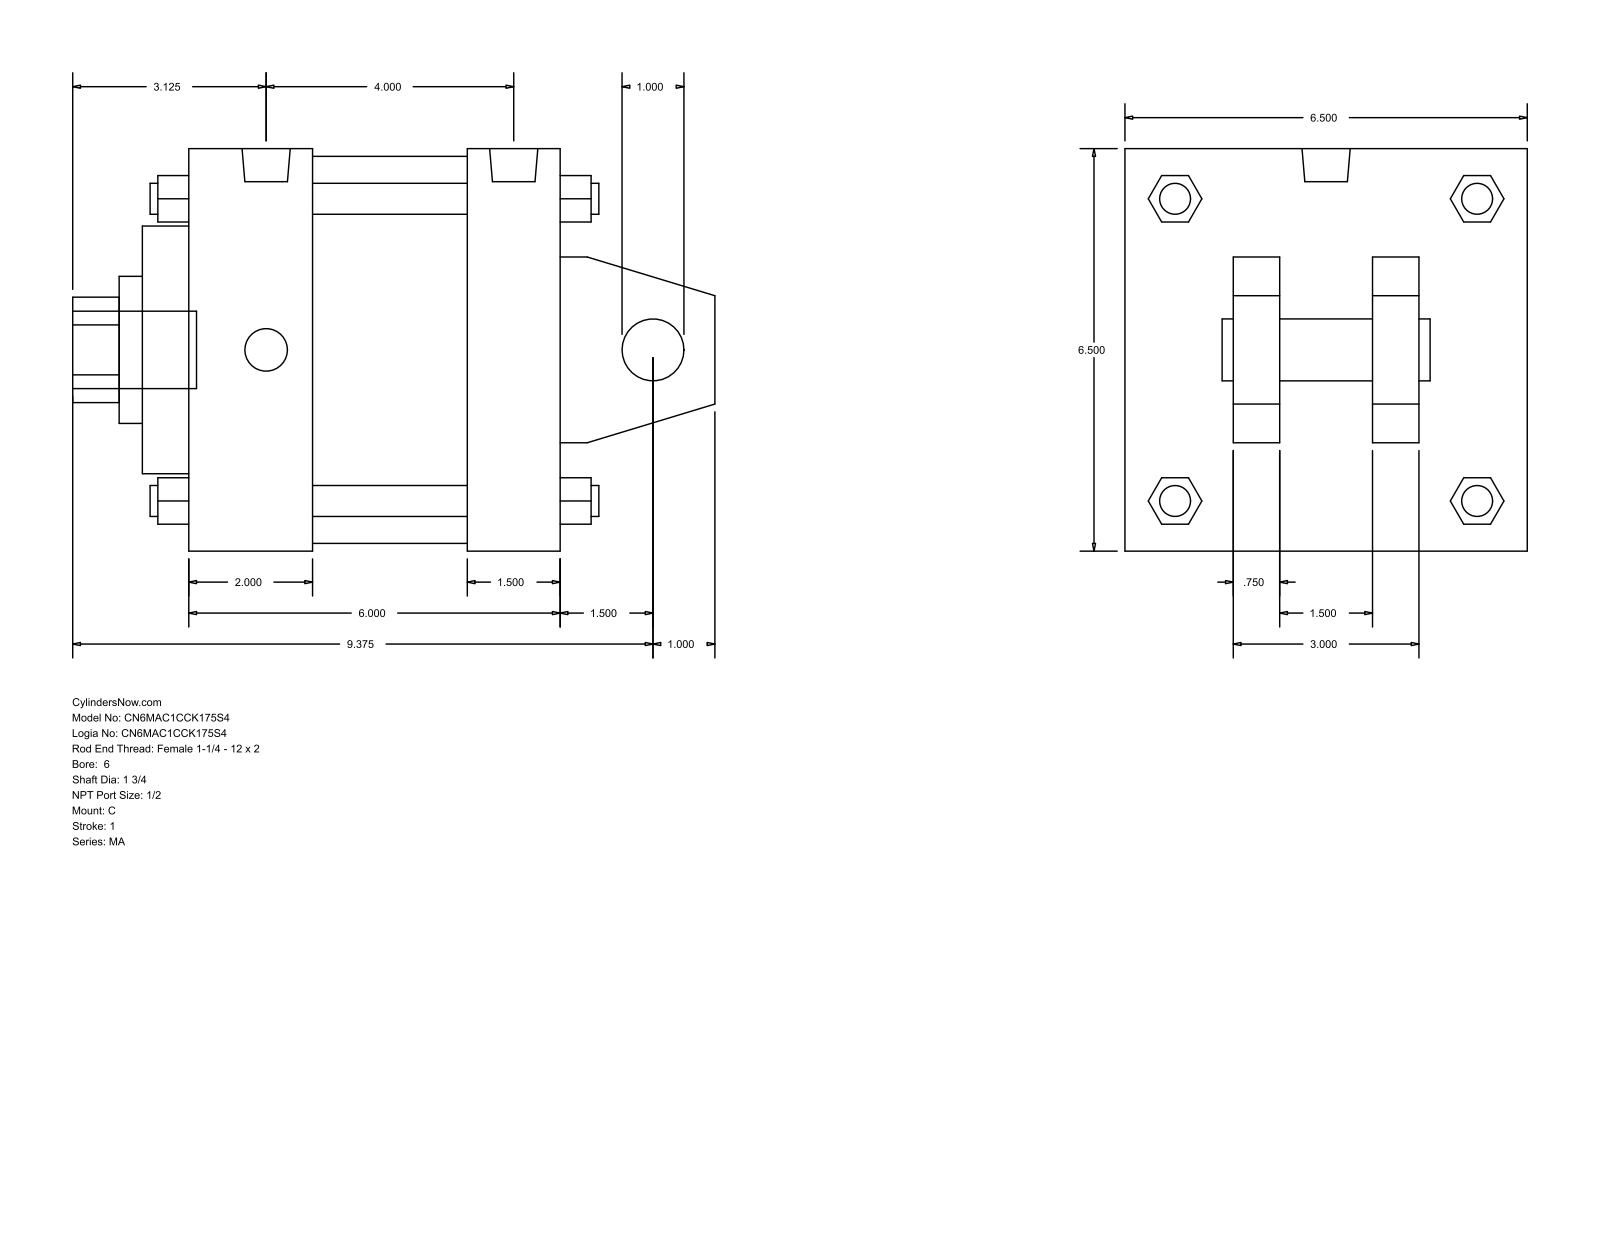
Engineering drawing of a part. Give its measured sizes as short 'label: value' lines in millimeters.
name: MA_C__0600_1.75
written by: GSSL Pune (CONFIG_CONTROL_DESIGN)
unit: mm
bodies: 0 solids, 141 faces (109 planar, 32 cylindrical, 0 other)
size: 263.52 × 165.1 × 165.1
holes: 1× ⌀25.4, 1× ⌀44.45, 1× ⌀60.33, 1× ⌀101.6, 1× ⌀158.75
bosses: 4× ⌀17.46, 4× ⌀12.7, 2× ⌀19.77, 1× ⌀31.75
rounds: 1× R21.63
face distances: 165.1, 152.41, 19.05, 38.1, 63.5, 101.6, 50.8, 44.45, 120.65, 57.15
